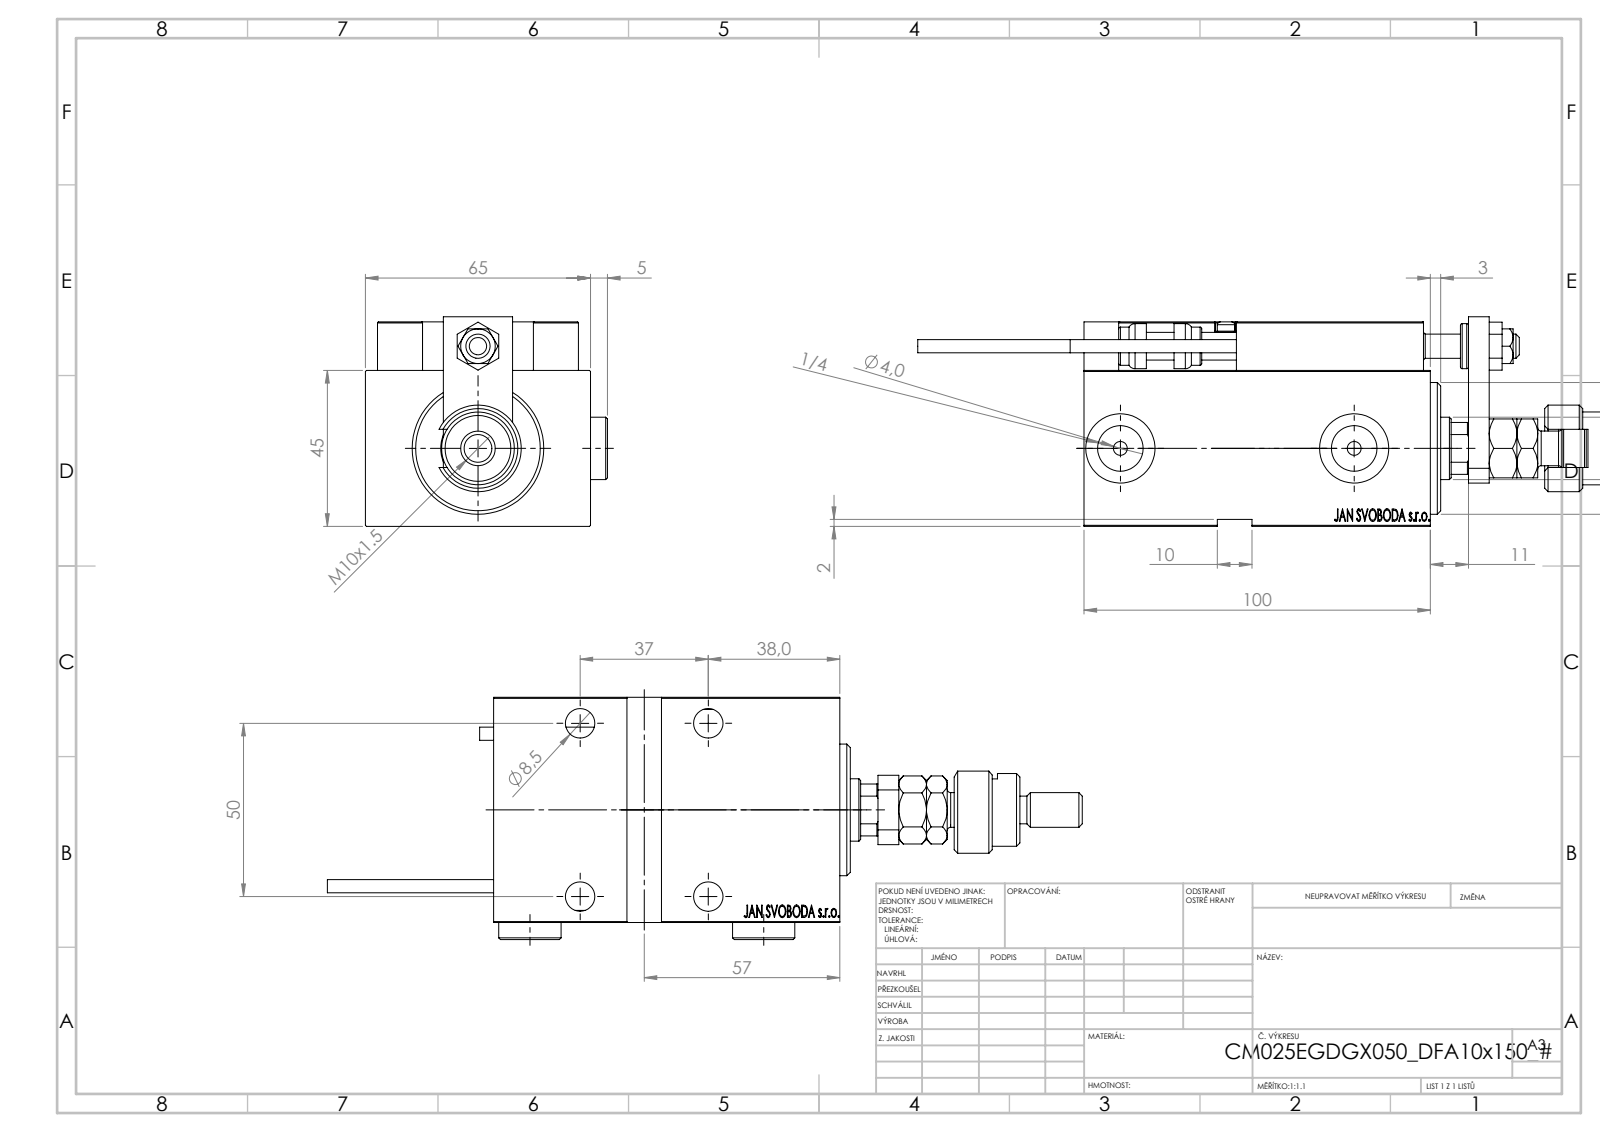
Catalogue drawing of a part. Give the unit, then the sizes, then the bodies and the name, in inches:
Units: inches
Overall size (bounding box): 8.583 × 2.752 × 2.382
Round holes (diameter × count): ⌀0.157 ×6, ⌀0.315 ×5, ⌀0.335 ×5, ⌀0.126 ×4, ⌀0.531 ×4, ⌀0.197 ×2, ⌀0.518 ×2, ⌀0.787 ×2, ⌀0.276 ×1, ⌀0.571 ×1, ⌀0.709 ×1, ⌀0.846 ×1
Round bosses / shafts (diameter × count): ⌀0.709 ×2, ⌀0.197 ×2, ⌀0.15 ×2, ⌀1.496 ×1, ⌀1.063 ×1, ⌀0.984 ×1, ⌀0.827 ×1, ⌀0.63 ×1
Partial cylindrical surfaces — rounded edges, fillets, slot ends (radius × count): R0.012 ×30, R0.118 ×2, R0.217 ×1, R0.335 ×1, R0.344 ×1
Main face-to-face distances: 1.772, 2.559, 0.551, 2.323, 0.236, 0.197, 0.512, 3.937, 0.748, 4.37
Hole centre spacings: 1.587, 0.448, 0.787, 0.984, 1.165, 1.169, 1.356, 1.42
Volume: 19.8 in³ · Surface area: 134.9 in²
Bodies: 28 solids, 1432 faces (632 planar, 211 cylindrical, 589 other)
Part name (STEP PRODUCT): SWITCH DIM B,W; MAGNET; KONCOVKA; ZARAZKA (+7 more)
STEP written by: SolidWorks 2019 (CONFIG_CONTROL_DESIGN)
